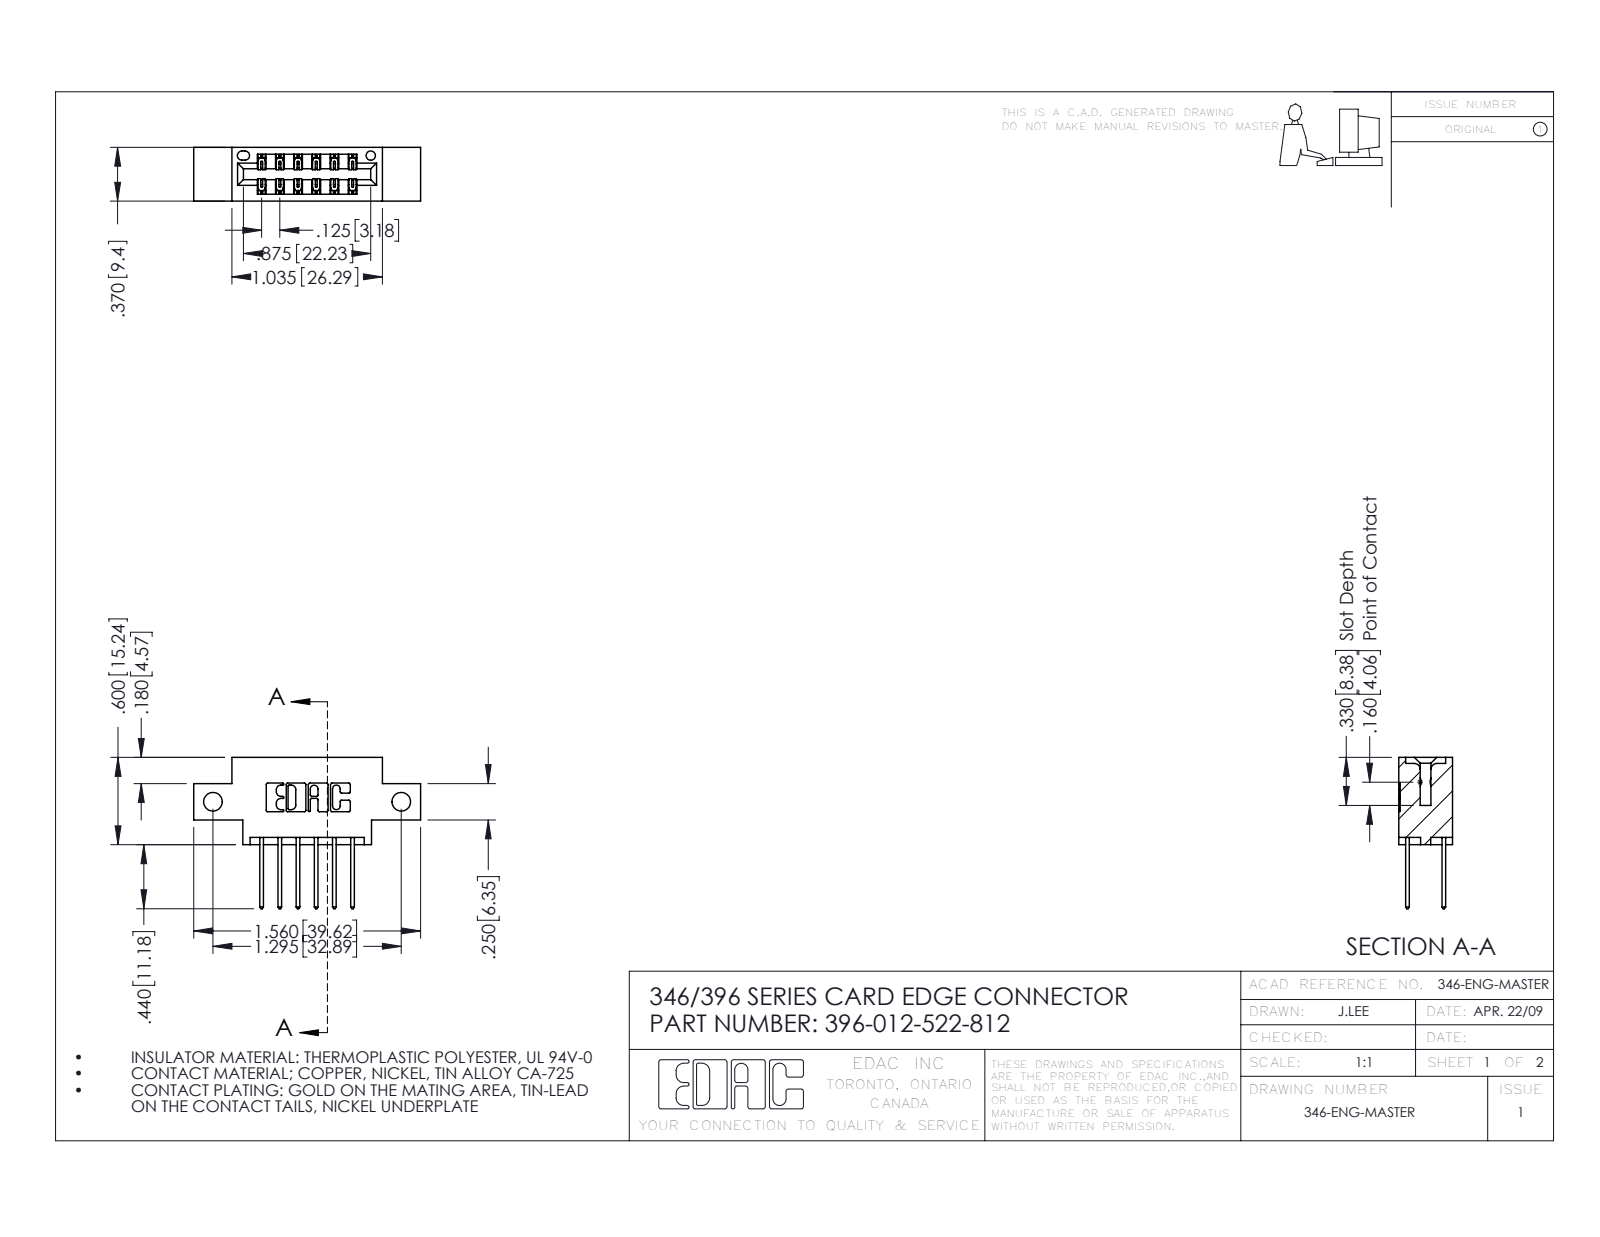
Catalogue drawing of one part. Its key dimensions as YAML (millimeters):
part_name: "345-292-001_345-293-122; 346 Part_0.170 Offset - Side Mount; 396-012-522-812"
step_written_by: "SolidWorks 2016 (CONFIG_CONTROL_DESIGN)"
units: millimeters
bodies: {solids: 13, faces: 750, planar: 500, cylindrical: 250, other: 0}
overall_size: [39.6, 26.4, 9.4]
volume: 3380
surface_area: 4255
round_holes:
  - {diameter: 3.3, count: 2}
  - {diameter: 1.6, count: 1}
partial_cylinders:
  - {radius: 0.3, count: 22}
  - {radius: 0.2, count: 18}
  - {radius: 0.3, count: 12}
  - {radius: 0.2, count: 6}
  - {radius: 0.8, count: 6}
  - {radius: 0.7, count: 3}
  - {radius: 0.4, count: 2}
  - {radius: 0.6, count: 2}
face_to_face_distances: [6.4, 9.4, 1.2, 8.2, 1.8, 7.6, 0.6, 7, 3.8, 5.6]
hole_center_spacings: [32.9]
